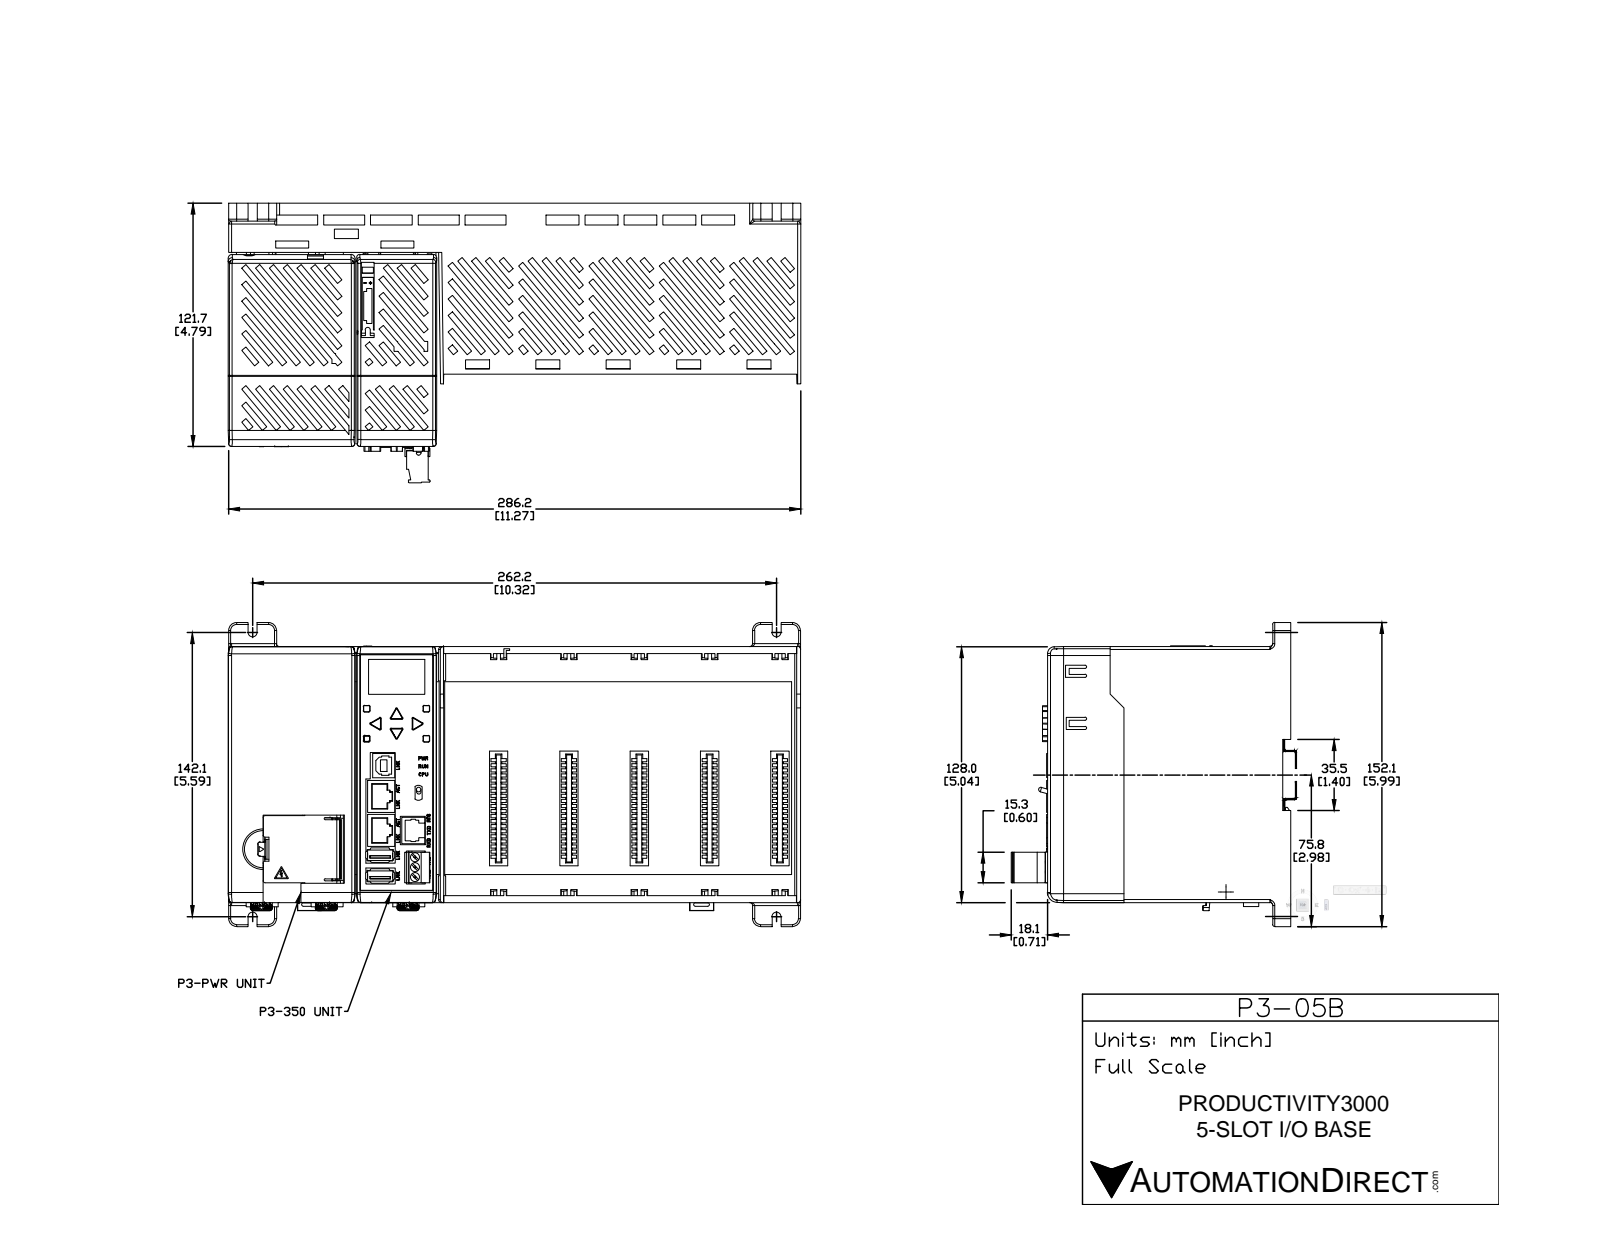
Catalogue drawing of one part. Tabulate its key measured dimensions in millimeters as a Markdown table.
| quantity | value |
| --- | --- |
| part name | P3-05B |
| STEP written by | SolidWorks 2009 (CONFIG_CONTROL_DESIGN) |
| units | millimeters |
| bodies | 1 solid, 396 faces (384 planar, 12 cylindrical, 0 other) |
| overall size | 286.3 × 151.9 × 88.9 |
| volume | 395 600 mm³ |
| surface area | 285 500 mm² |
| partial cylindrical surfaces (radius × count) | 4.1 × 8, 2.3 × 4 |
| main face-to-face distances | 1.9, 10.9, 15.8, 13.9, 3, 1.9, 12.8, 128, 126.1, 9 |
